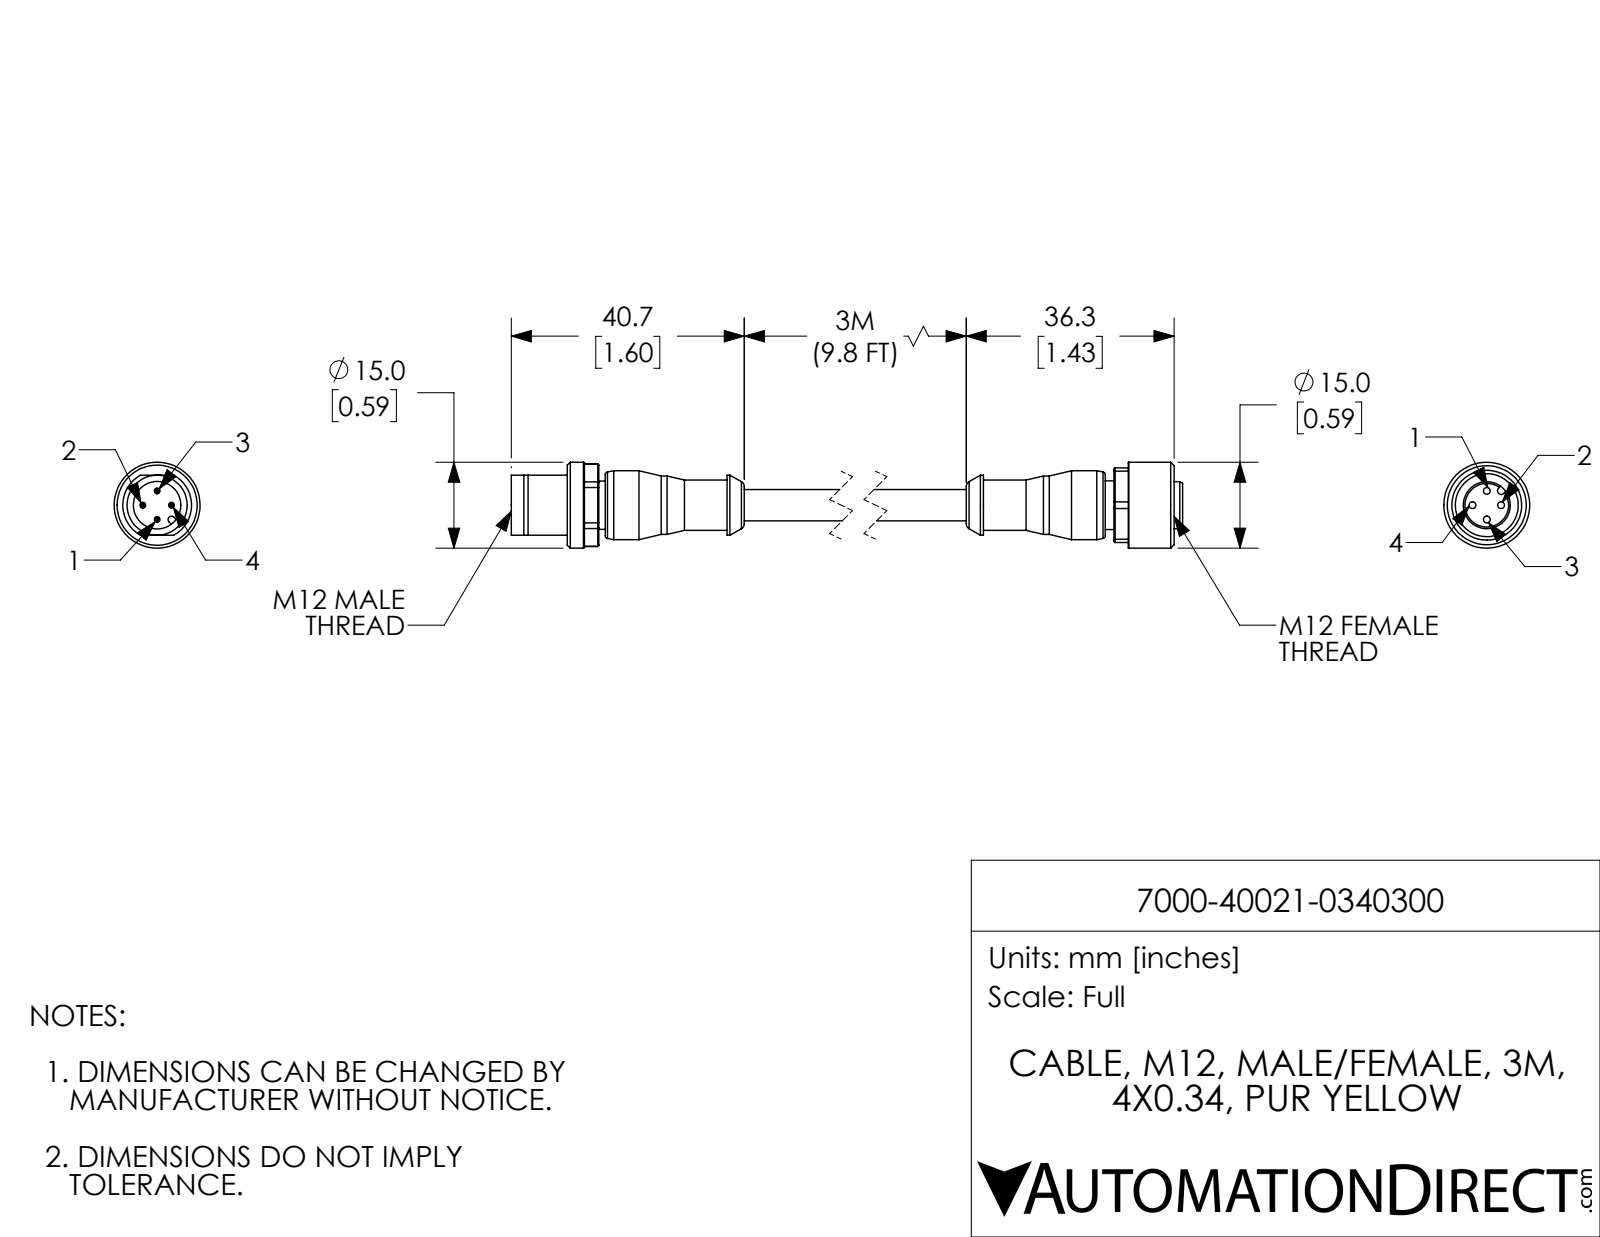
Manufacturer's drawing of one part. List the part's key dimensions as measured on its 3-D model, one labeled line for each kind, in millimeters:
Part name (STEP PRODUCT): 7000-40021-0340300; 7000-40021-0340300_MALE; 7000-40021-0340300_FEMALE
STEP written by: SolidWorks 2021 (CONFIG_CONTROL_DESIGN)
Units: millimetres
Bodies: 2 solids, 188 faces (58 planar, 69 cylindrical, 61 other)
Overall size (bounding box): 130.5 × 15 × 15
Volume: 8 000 mm³ · Surface area: 5 116 mm²
Round holes (diameter × count): ⌀1.2 ×4, ⌀8.3 ×1, ⌀11 ×1
Round bosses / shafts (diameter × count): ⌀1 ×4, ⌀15 ×1, ⌀12 ×1, ⌀10.5 ×1, ⌀10.2 ×1, ⌀8.8 ×1, ⌀8.5 ×1, ⌀8.4 ×1
Partial cylindrical surfaces — rounded edges, fillets, slot ends (radius × count): R0.6 ×1, R0.7 ×1, R7.2 ×1
Main face-to-face distances: 12, 13, 3, 103.2, 10.5, 112.6, 56.3, 108.7, 7.5, 1.5
Hole centre spacings: 2.5, 3.5, 5
